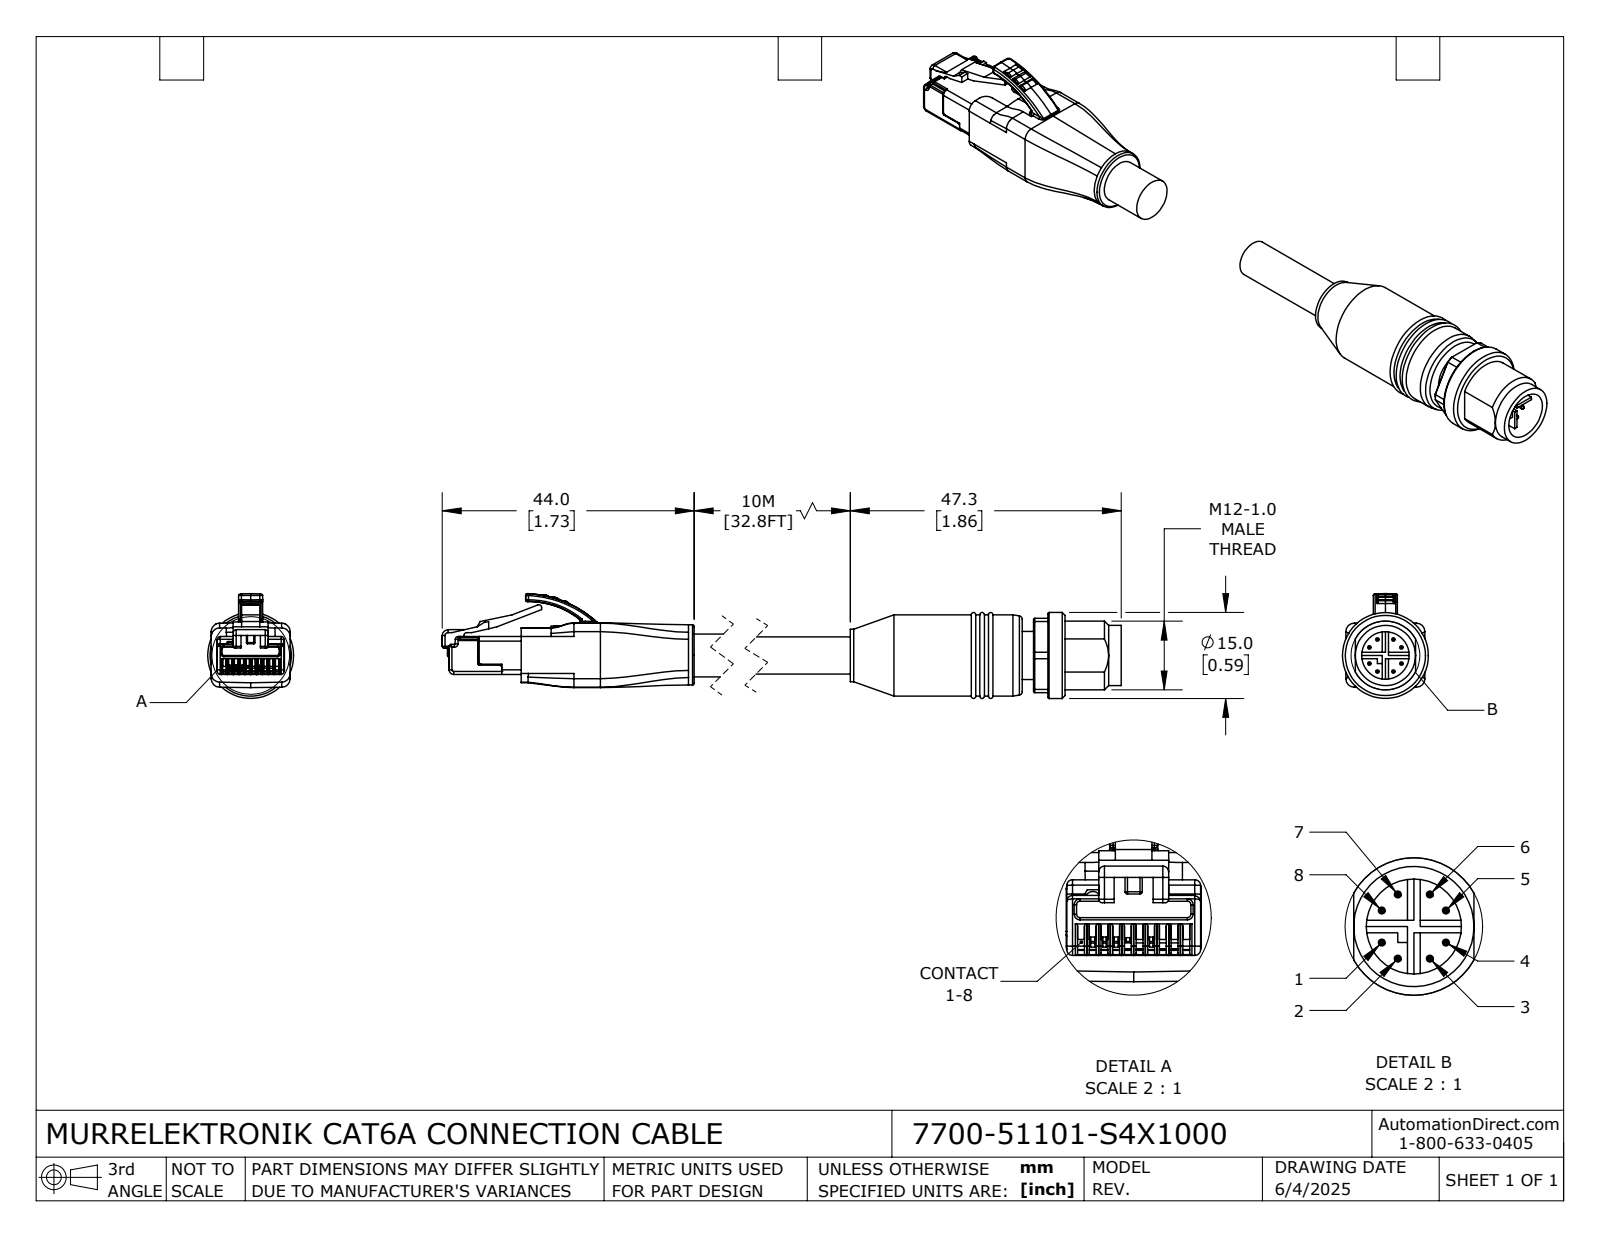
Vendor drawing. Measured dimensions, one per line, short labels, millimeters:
name: 7700-51101-S4X1000_RJ45; 7700-51101-S4X1000; 7700-51101-S4X1000_MALE
written by: SolidWorks 2024 (CONFIG_CONTROL_DESIGN)
unit: mm
bodies: 2 solids, 752 faces (352 planar, 226 cylindrical, 174 other)
size: 144.3 × 18.29 × 15
volume: 11 935 mm³; area: 5 963 mm²
holes: 1× ⌀8.3
bosses: 8× ⌀0.6, 2× ⌀10.5, 1× ⌀15, 1× ⌀14.2, 1× ⌀9.2, 1× ⌀8.4, 1× ⌀7.5, 1× ⌀6.5
rounds: 61× R0.2, 25× R0.5, 14× R0.3, 9× R1.5, 5× R0.8, 2× R0.54, 2× R5, 1× R0.13
face distances: 13.8, 3.85, 4.7, 2, 1.65, 12.15, 6.35, 7.45, 5.8, 2.75
